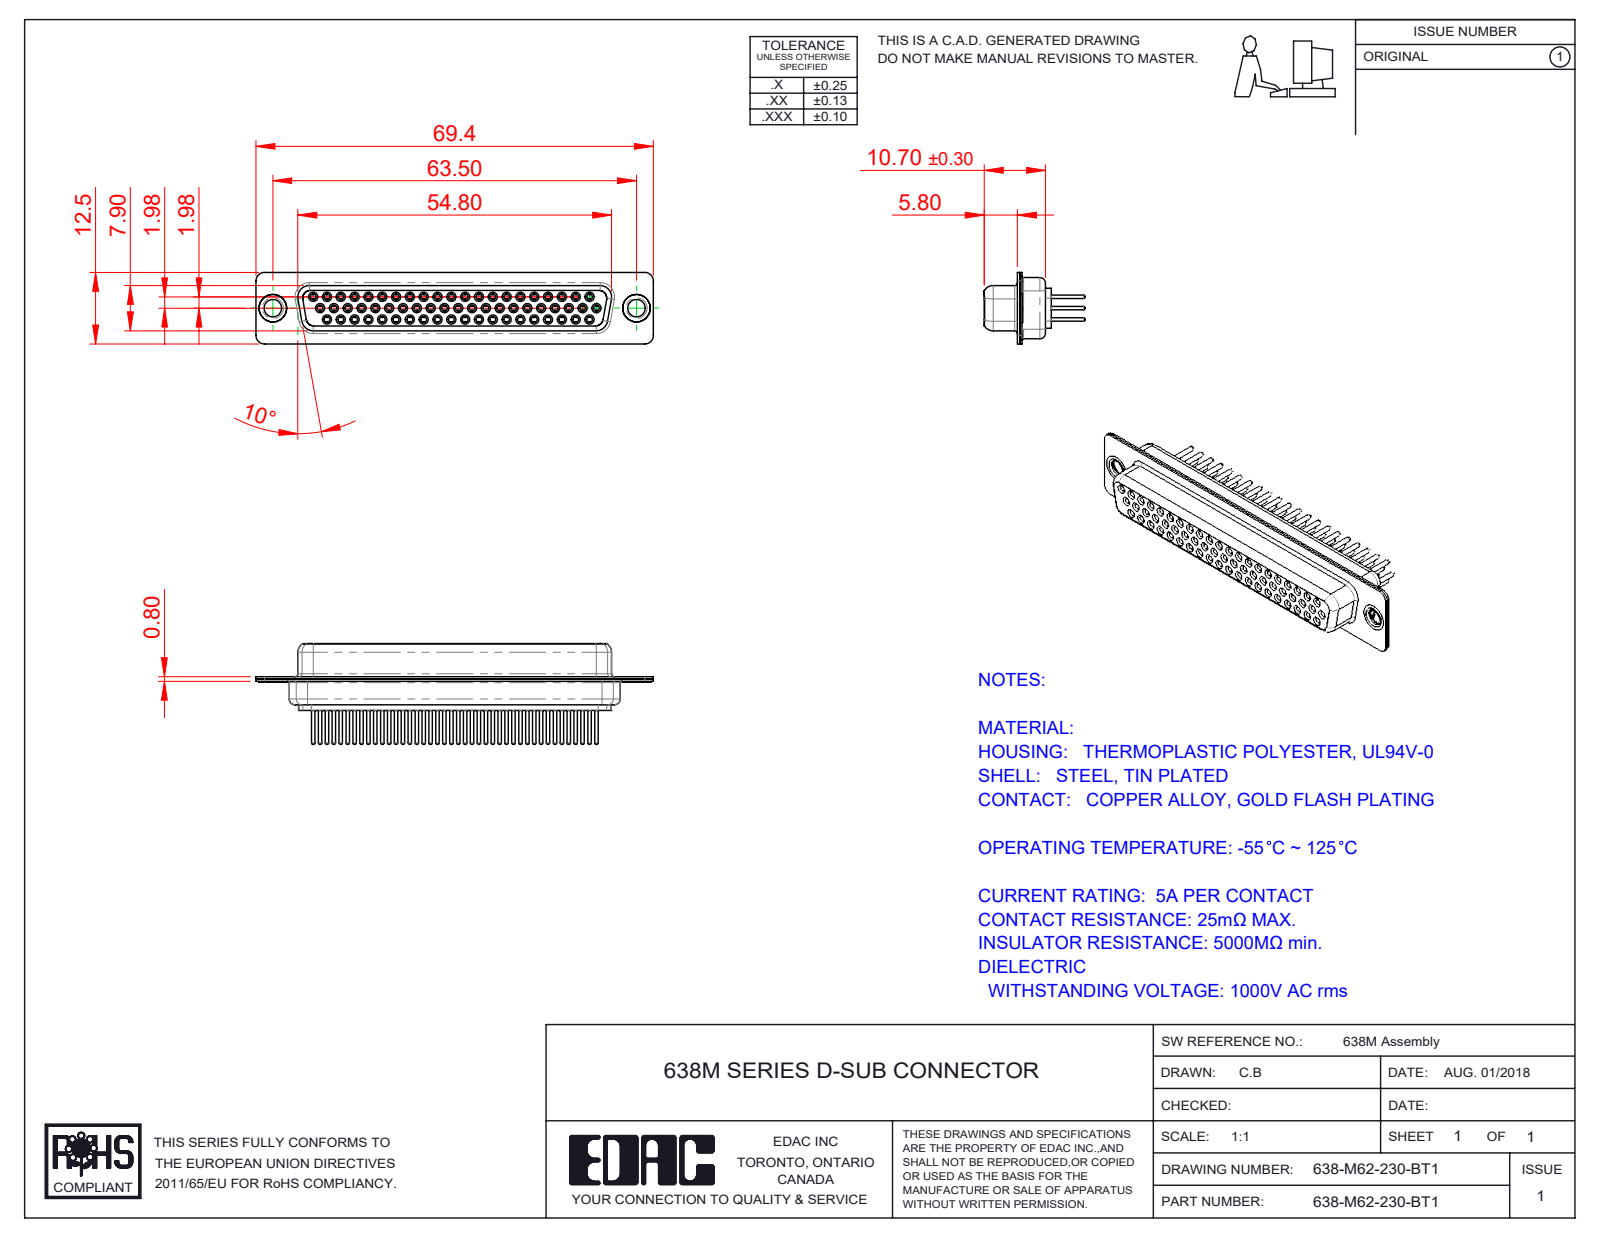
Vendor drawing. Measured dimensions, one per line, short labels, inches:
name: 638M Shell Rear_62 Contacts; 638M Housing_62 Contacts; 638M Contact Row 2_30; 638M Thru Hole Rivet (+4 more)
written by: SolidWorks 2020 (CONFIG_CONTROL_DESIGN)
unit: in
bodies: 67 solids, 3663 faces (997 planar, 1299 cylindrical, 1367 other)
size: 2.732 × 0.693 × 0.492
volume: 0.299 in³; area: 25.26 in²
holes: 62× ⌀0.039, 62× ⌀0.043, 62× ⌀0.067, 62× ⌀0.071, 62× ⌀0.079, 2× ⌀0.12, 2× ⌀0.157, 2× ⌀0.189
bosses: 62× ⌀0.087, 62× ⌀0.063, 62× ⌀0.059, 62× ⌀0.024, 2× ⌀0.197, 2× ⌀0.193, 2× ⌀0.14
rounds: 16× R0.059, 12× R0.079, 8× R0.053, 8× R0.063, 4× R0.01, 4× R0.02, 4× R0.024, 4× R0.026
face distances: 0.016, 0.055, 0.018, 0.333, 0.35, 0.071, 0.039, 0.244, 0.278, 0.073
hole spacings: 0.285, 0.091, 0.095, 0.163, 0.38, 0.19, 0.57, 0.665
